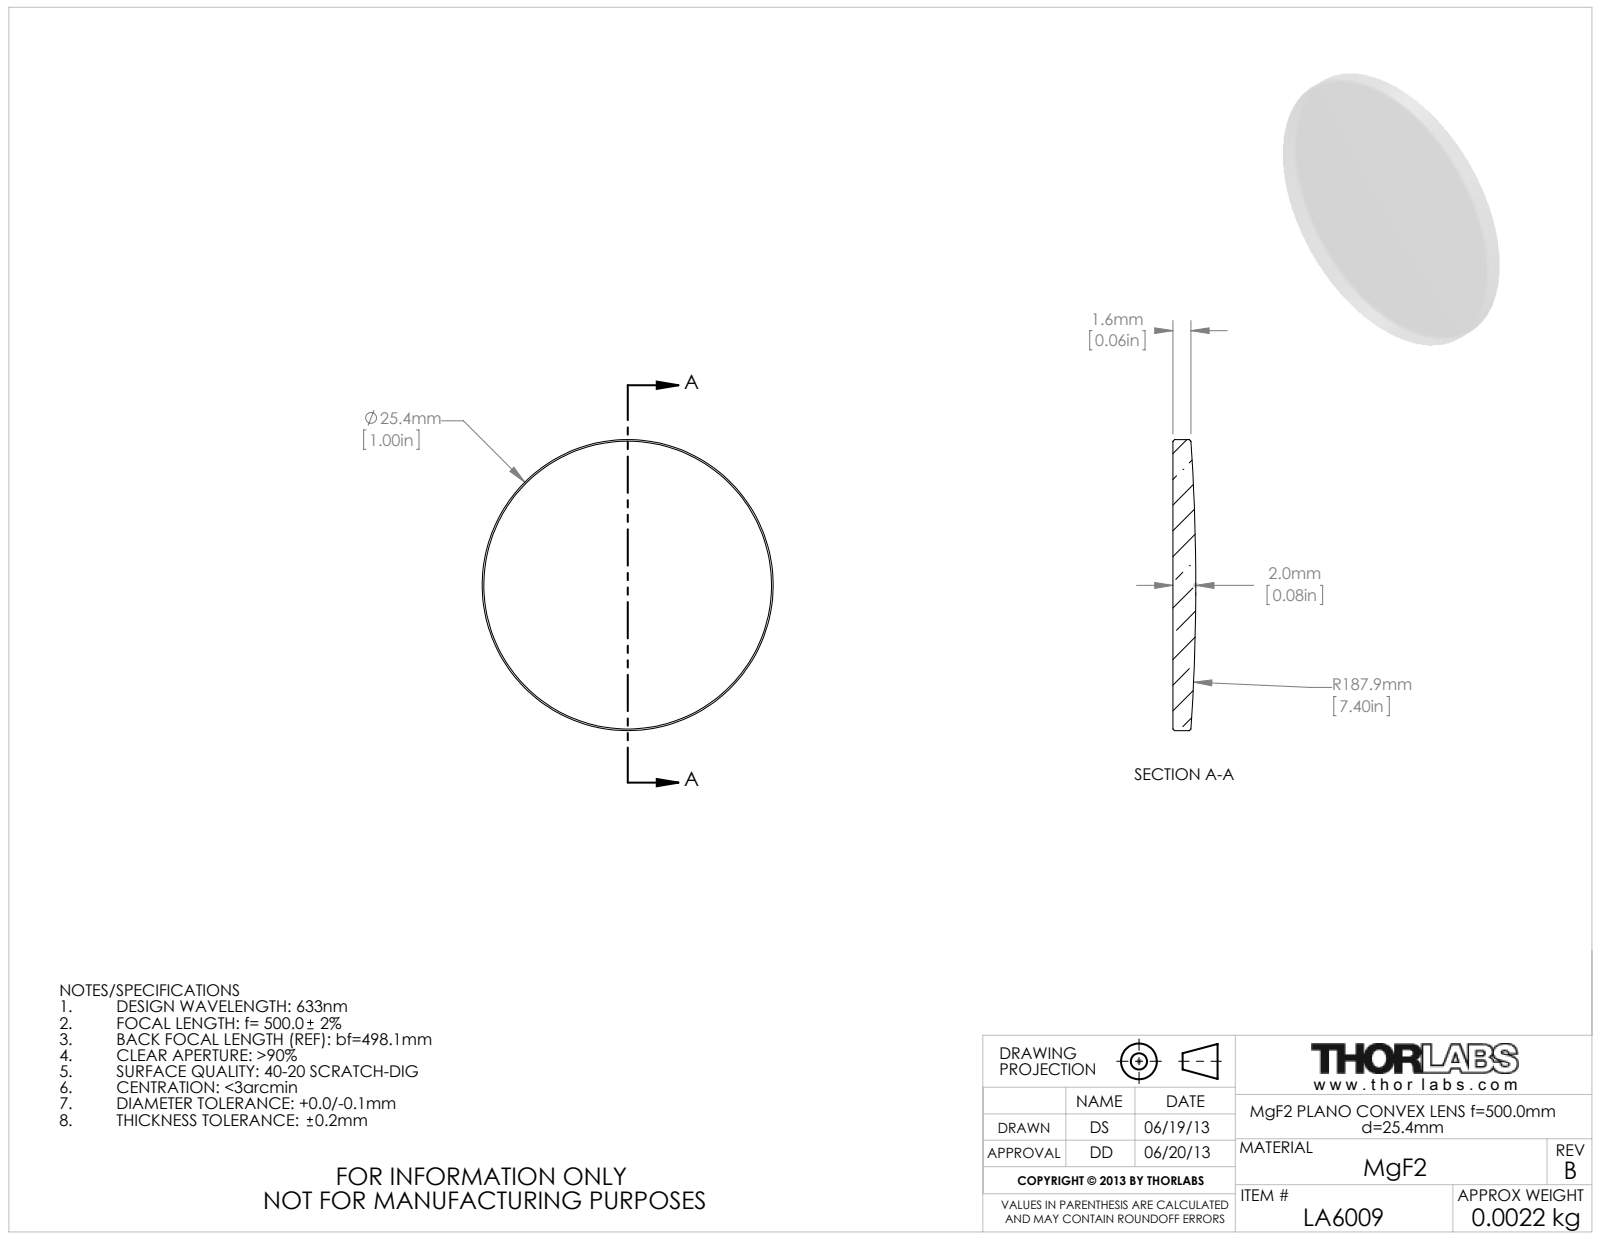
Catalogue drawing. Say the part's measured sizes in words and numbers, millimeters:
The part is named "7260-E0W". Its 3-D file was written by "SolidWorks 2007 (AUTOMOTIVE_DESIGN)". It is 0 solids with 5 faces: 1 planar, 2 cylindrical and 2 other. Overall it measures 25.4 by 25.4 by 2 millimeters. Round bosses or shafts: 1 of diameter 25.4.
